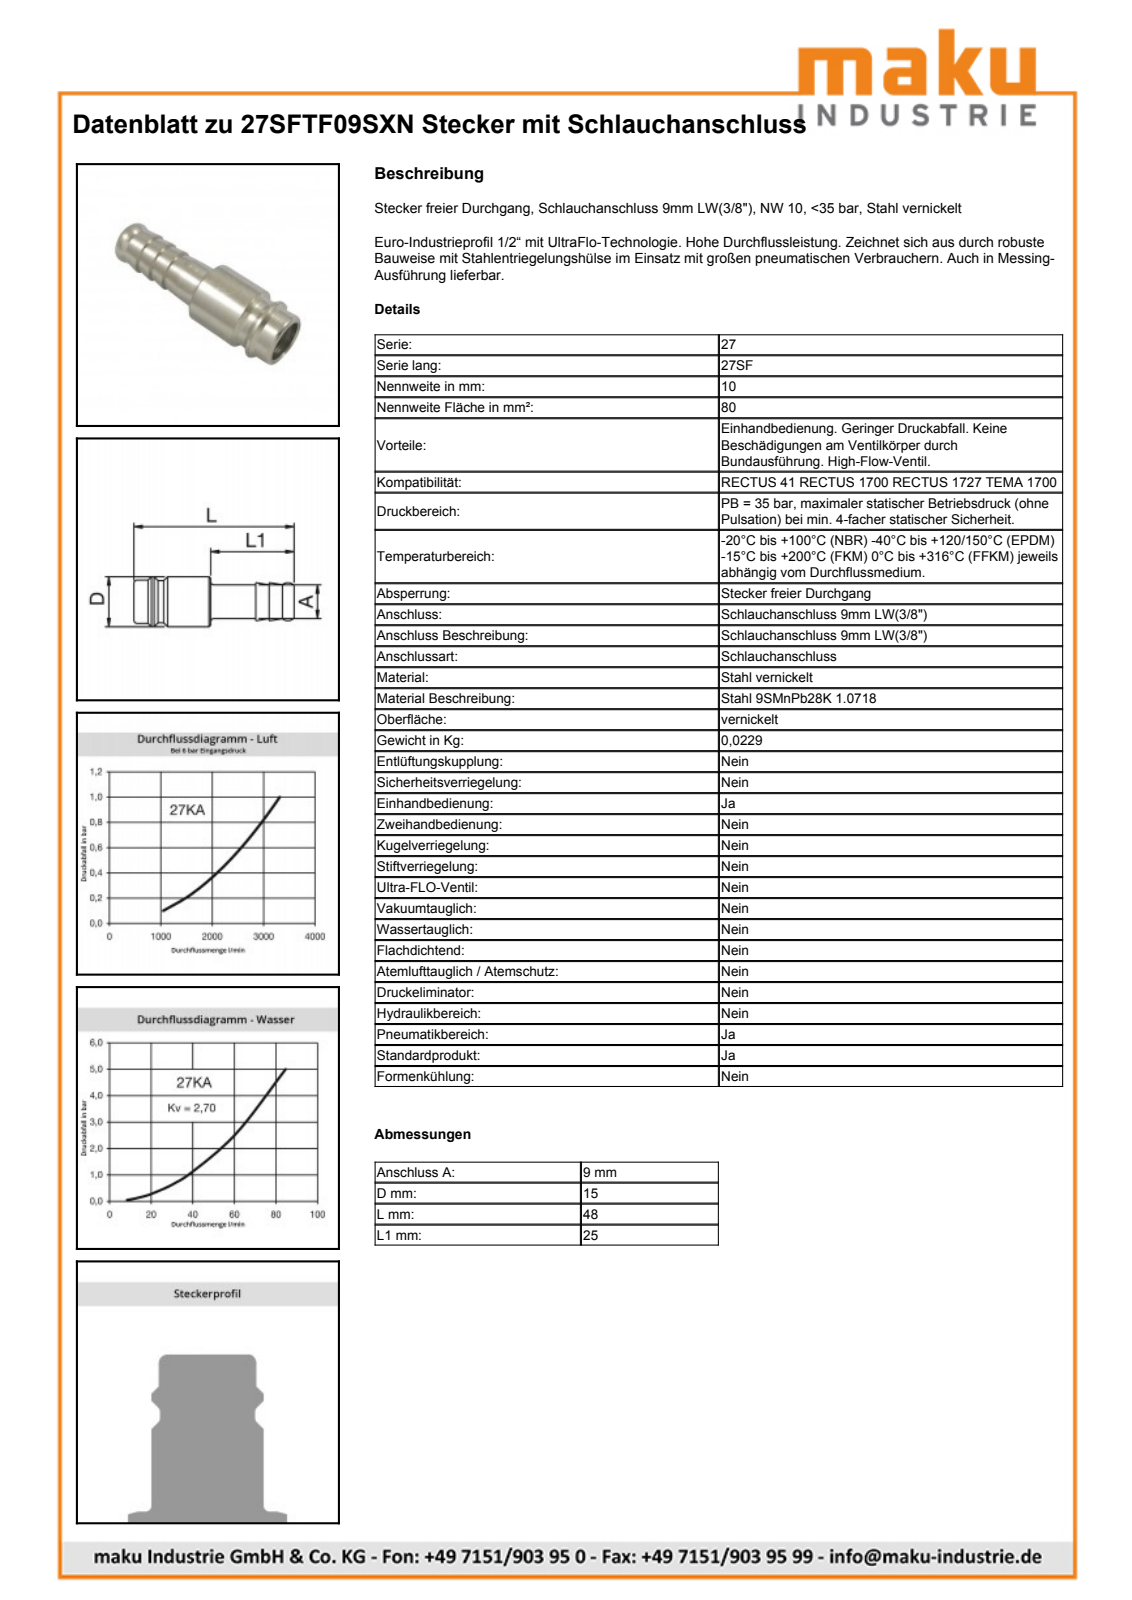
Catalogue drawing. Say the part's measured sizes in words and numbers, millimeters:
The part is named "D103751". Its 3-D file was written by "Autodesk Inventor 2011 (AUTOMOTIVE_DESIGN)". It is 1 solid with 26 faces: 4 planar, 7 cylindrical and 15 other. Overall it measures 48 by 15 by 15 millimeters. Its volume is 2 785 cubic millimeters and its surface area 3 290 square millimeters. Round holes: 1 of diameter 7, 1 of diameter 10. Round bosses or shafts: 1 of diameter 15, 1 of diameter 13, 1 of diameter 12.65, 1 of diameter 9.1. The main face-to-face distances are 25, 23, 48, 36.5, 13.5, 11.5.
